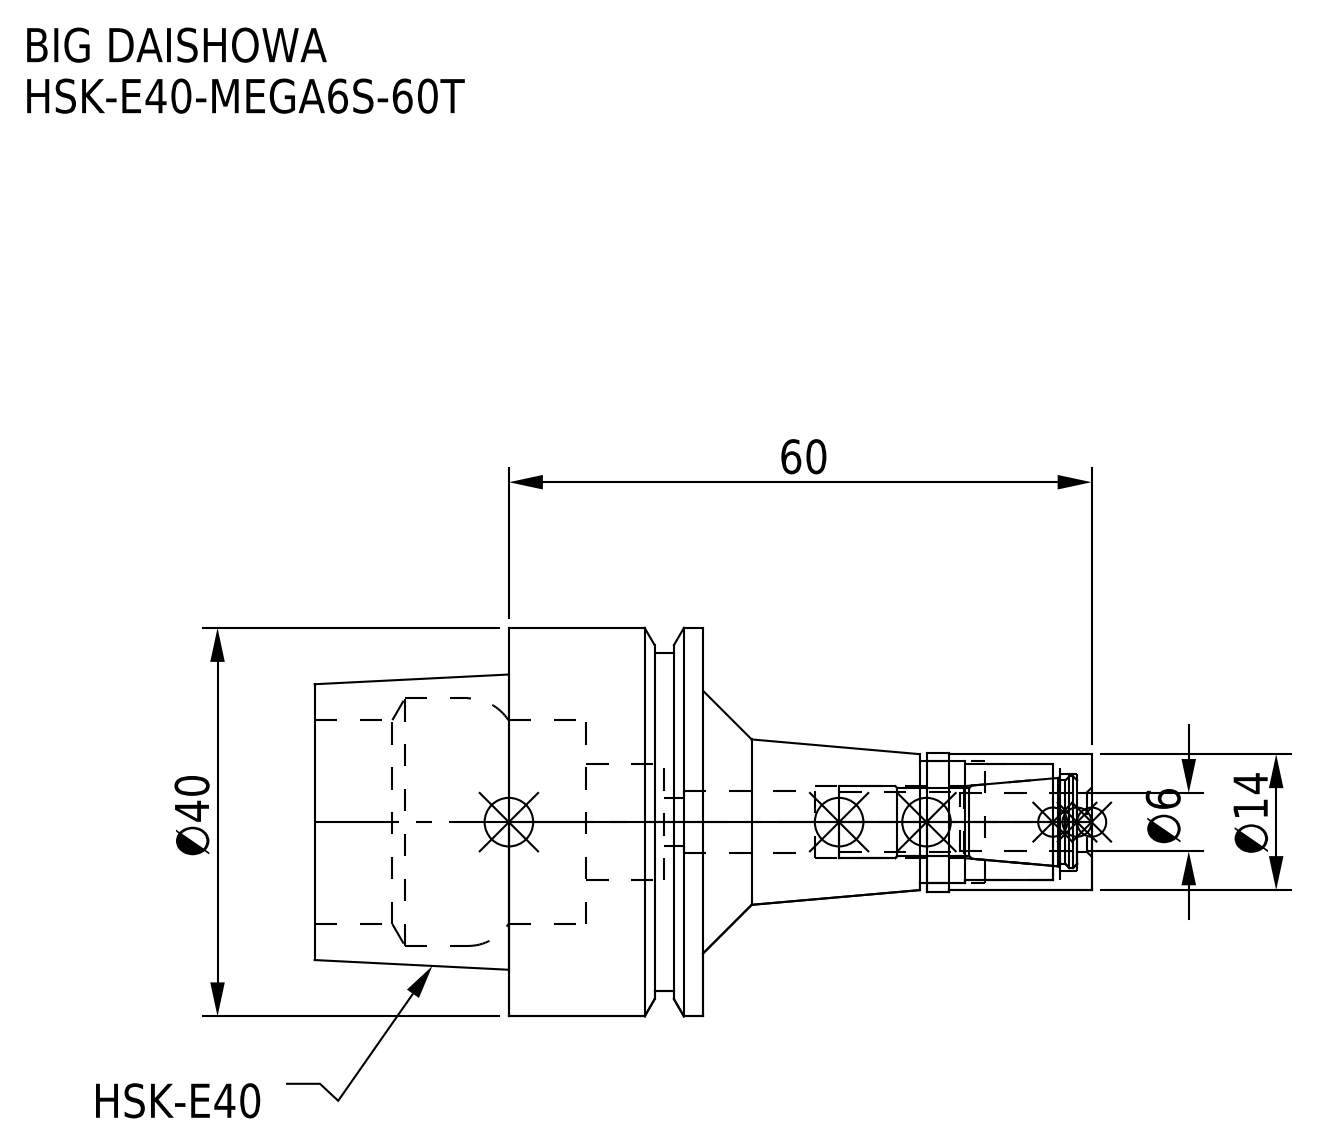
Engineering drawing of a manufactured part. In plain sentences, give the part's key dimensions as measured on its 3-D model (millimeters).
The part is named "HSK-E40-MEGA6S-60T-060-FreeParts; HSK-E40-MEGA6S-60T_1.stp; HSK-E40-MEGA6S-60T; DXF_TEMP_ASSY_ASM_4_ASM.stp (+3 more)". Its 3-D file was written by "SolidWorks 2019 (CONFIG_CONTROL_DESIGN)". It is 2 solids with 74 faces: 18 planar, 38 cylindrical and 18 other. Overall it measures 80 by 40 by 40 millimeters. Its volume is 31 688 cubic millimeters and its surface area 13 504 square millimeters. Round holes: 1 of diameter 5, 1 of diameter 6.1, 1 of diameter 6.4, 1 of diameter 7.4, 1 of diameter 10, 1 of diameter 12, 1 of diameter 12.5, 1 of diameter 21, 1 of diameter 25.5. Round bosses or shafts: 1 of diameter 40, 1 of diameter 34.8, 1 of diameter 14.3, 1 of diameter 14. The main face-to-face distances are 20, 40, 12.05, 7.95, 27.95, 17, 43, 2, 52.05, 60.
